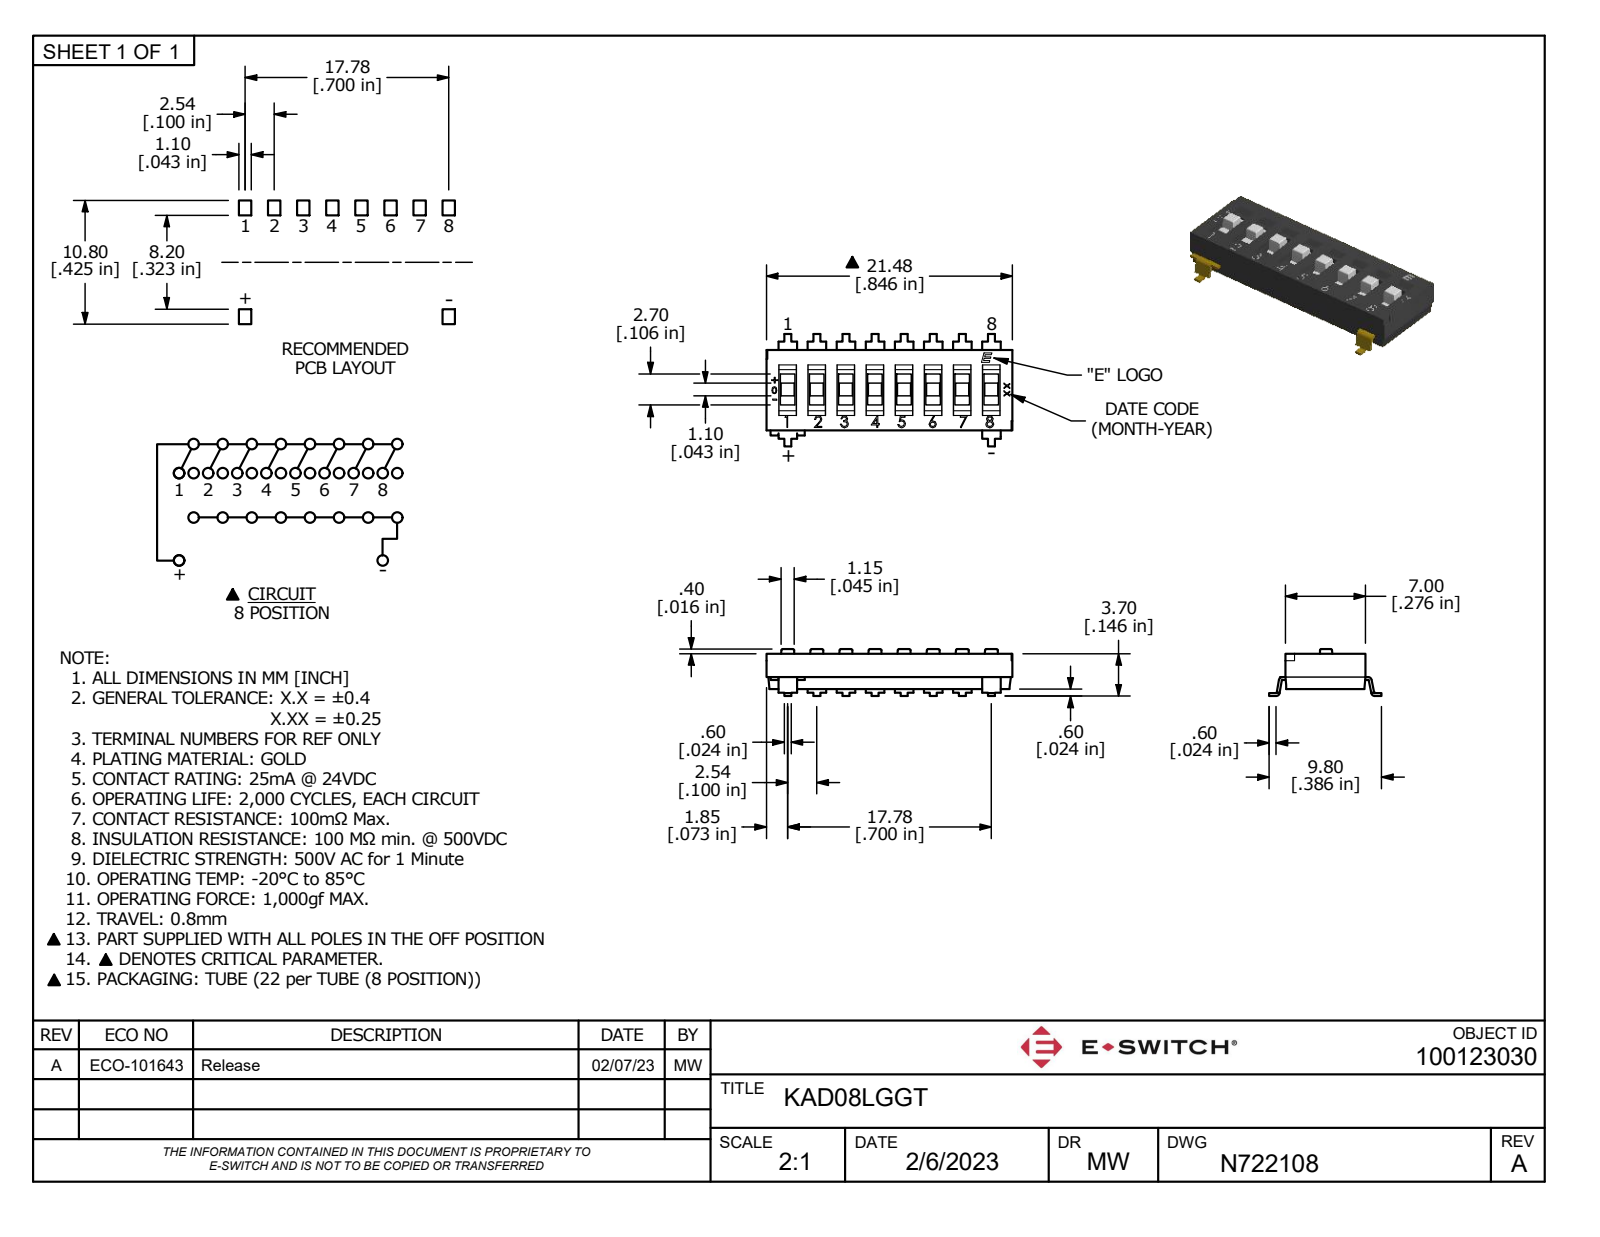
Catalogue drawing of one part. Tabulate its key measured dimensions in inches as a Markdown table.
| quantity | value |
| --- | --- |
| part name | KAD08LGGT |
| STEP written by | Autodesk Inventor 2022 (AUTOMOTIVE_DESIGN) |
| units | inches |
| bodies | 1 solid, 571 faces (428 planar, 72 cylindrical, 71 other) |
| overall size | 0.846 × 0.386 × 0.161 |
| volume | 0.028 in³ |
| surface area | 0.995 in² |
| partial cylindrical surfaces (radius × count) | 0.004 × 20, 0.012 × 4 |
| main face-to-face distances | 0.122, 0.276, 0.1, 0.2, 0.106, 0.031, 0.3, 0.016, 0.846, 0.059 |
